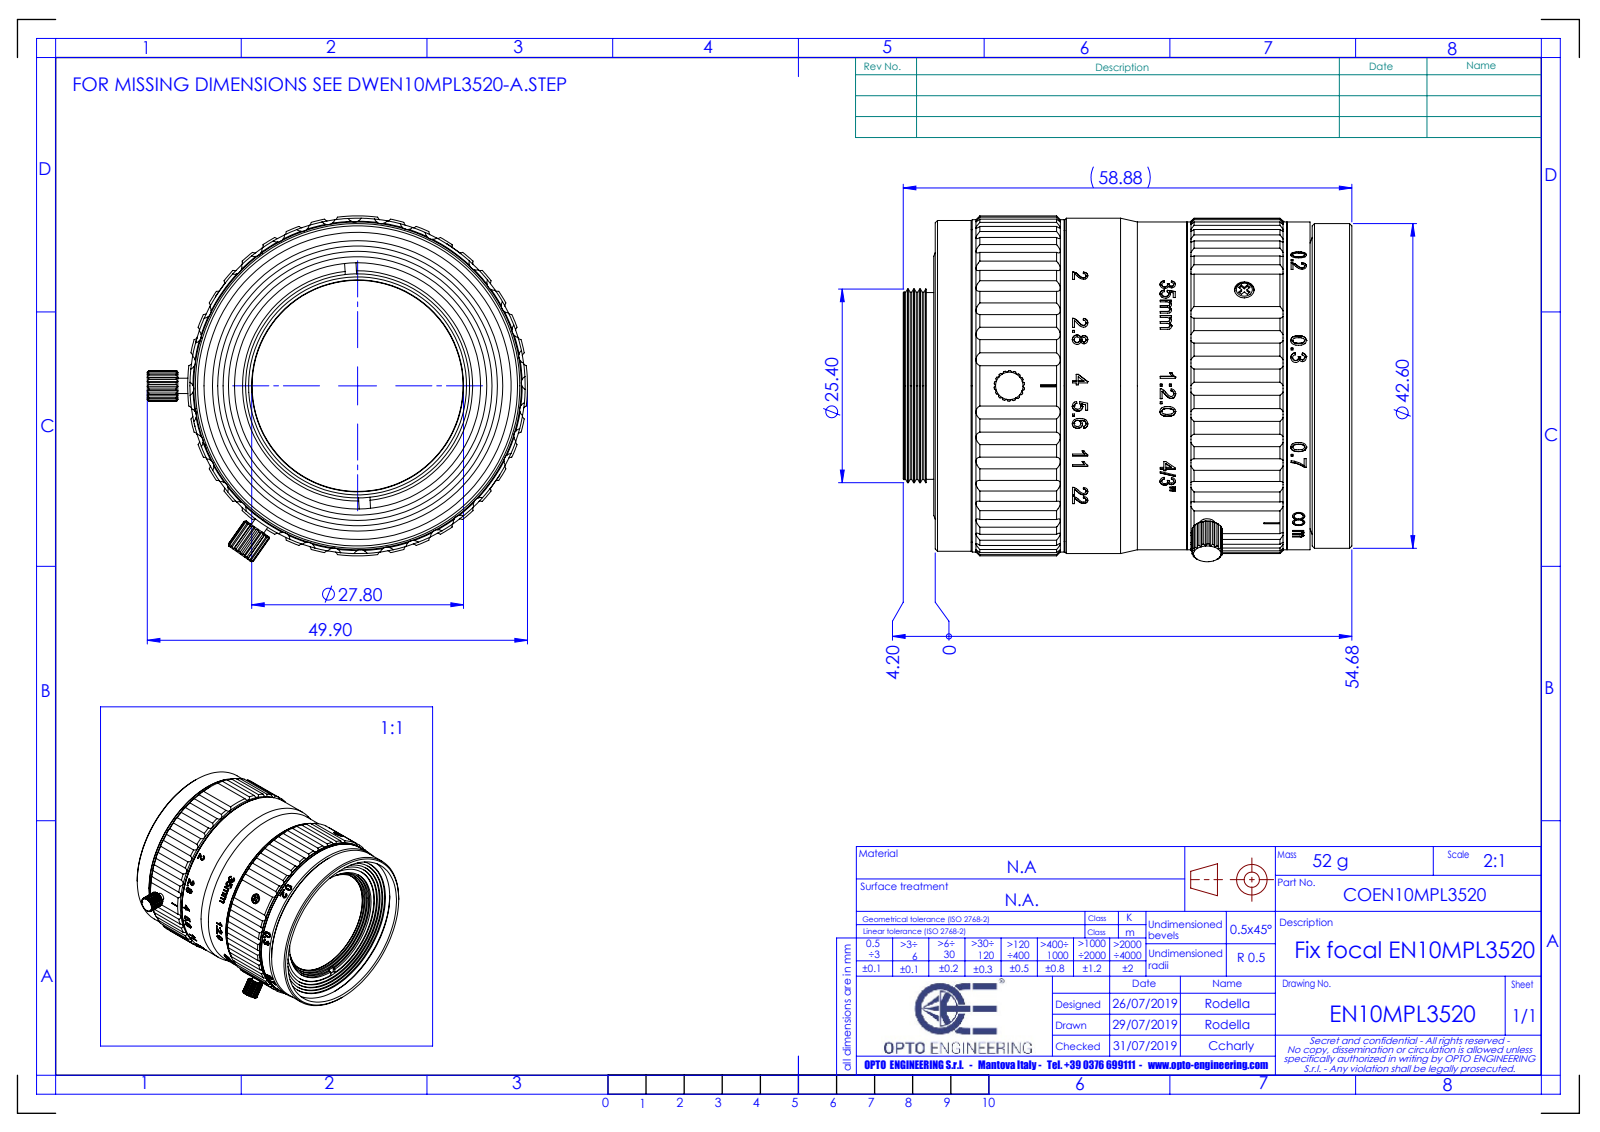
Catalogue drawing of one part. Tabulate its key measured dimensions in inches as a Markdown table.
| quantity | value |
| --- | --- |
| part name | 6692_ASM_ASM |
| STEP written by | PRO/ENGINEER BY PARAMETRIC TECHNOLOGY CORPORATION, 2011310 (AUTOMOTIVE_DESIGN) |
| units | inches |
| bodies | 1 solid, 2509 faces (870 planar, 831 cylindrical, 808 other) |
| overall size | 2.318 × 1.965 × 1.786 |
| volume | 3.174 in³ |
| surface area | 73.25 in² |
| round holes (diameter × count) | 0.047 × 22, 0.063 × 8, 0.102 × 7, 0.059 × 6, 0.049 × 3, 0.071 × 3, 0.106 × 3, 0.031 × 2, 0.039 × 2, 0.043 × 1, 0.098 × 1, 0.5 × 1 |
| round bosses / shafts (diameter × count) | 0.098 × 14, 0.055 × 7, 0.047 × 5, 0.067 × 3, 0.079 × 2, 1.732 × 1, 1.717 × 1, 1.709 × 1 |
| partial cylindrical surfaces (radius × count) | 0.039 × 94, 0.049 × 19, 0.02 × 14, 0.079 × 11, 0.024 × 10, 0.033 × 5, 0.291 × 5, 0.443 × 5 |
| main face-to-face distances | 0.118, 0.877, 0.276, 0.459, 0.993, 0.11, 1.827, 0.363, 0.473, 0.481 |
| hole center spacings | 0.697, 0.394, 0.243, 0.637, 0.749, 0.463, 1.108, 1.207 |
